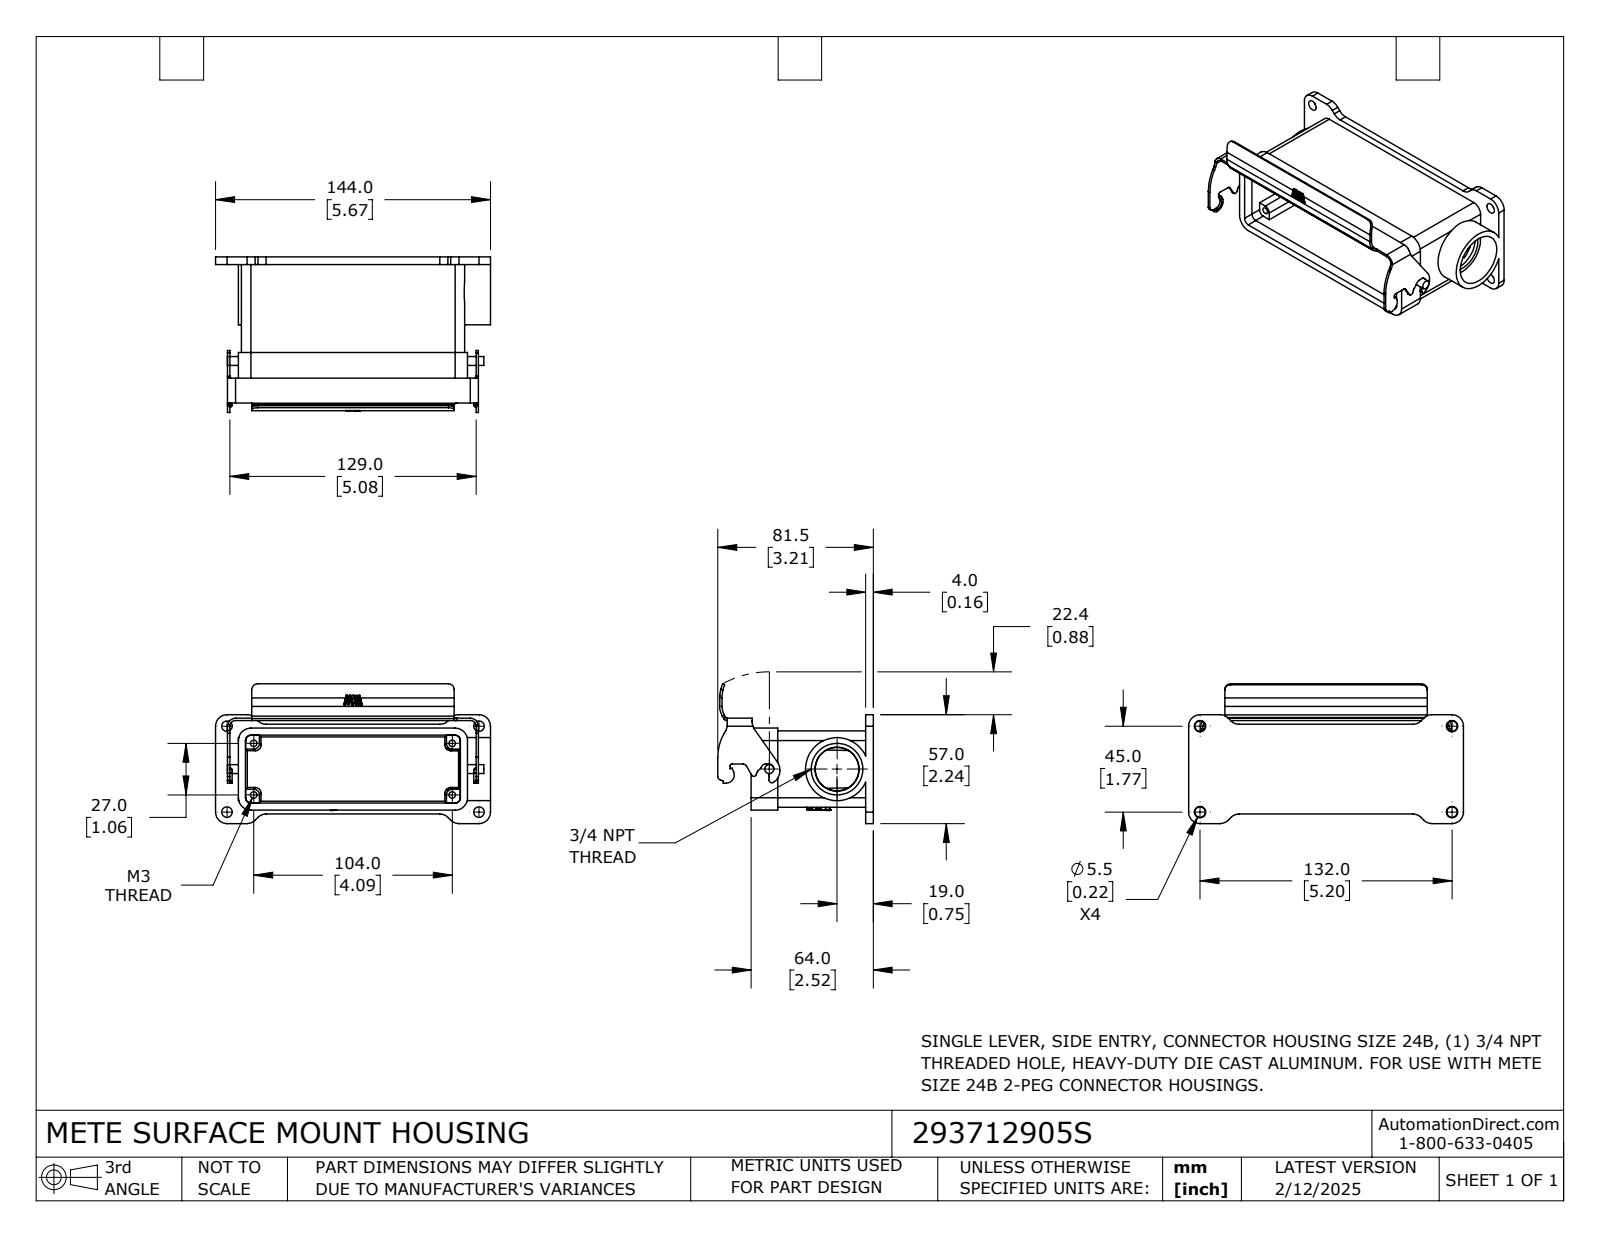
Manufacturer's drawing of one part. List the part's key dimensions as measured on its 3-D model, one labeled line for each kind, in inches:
Part name (STEP PRODUCT): 293712905S
STEP written by: SolidWorks 2024 (CONFIG_CONTROL_DESIGN)
Units: inches
Bodies: 1 solid, 334 faces (158 planar, 158 cylindrical, 18 other)
Overall size (bounding box): 5.669 × 3.207 × 2.881
Volume: 6.189 in³ · Surface area: 101.5 in²
Round holes (diameter × count): ⌀0.134 ×4, ⌀0.906 ×1, ⌀1.063 ×1
Round bosses / shafts (diameter × count): ⌀1.299 ×1, ⌀0.185 ×1
Partial cylindrical surfaces — rounded edges, fillets, slot ends (radius × count): R0.008 ×42, R0.236 ×14, R0.118 ×9, R0.039 ×6, R0.11 ×4, R0.197 ×4, R0.256 ×4, R0.079 ×3
Main face-to-face distances: 0.157, 1.575, 0.059, 0.047, 1.634, 0.224, 1.79, 1.837, 0.215, 0.262
Hole centre spacings: 1.063, 4.094, 4.23
